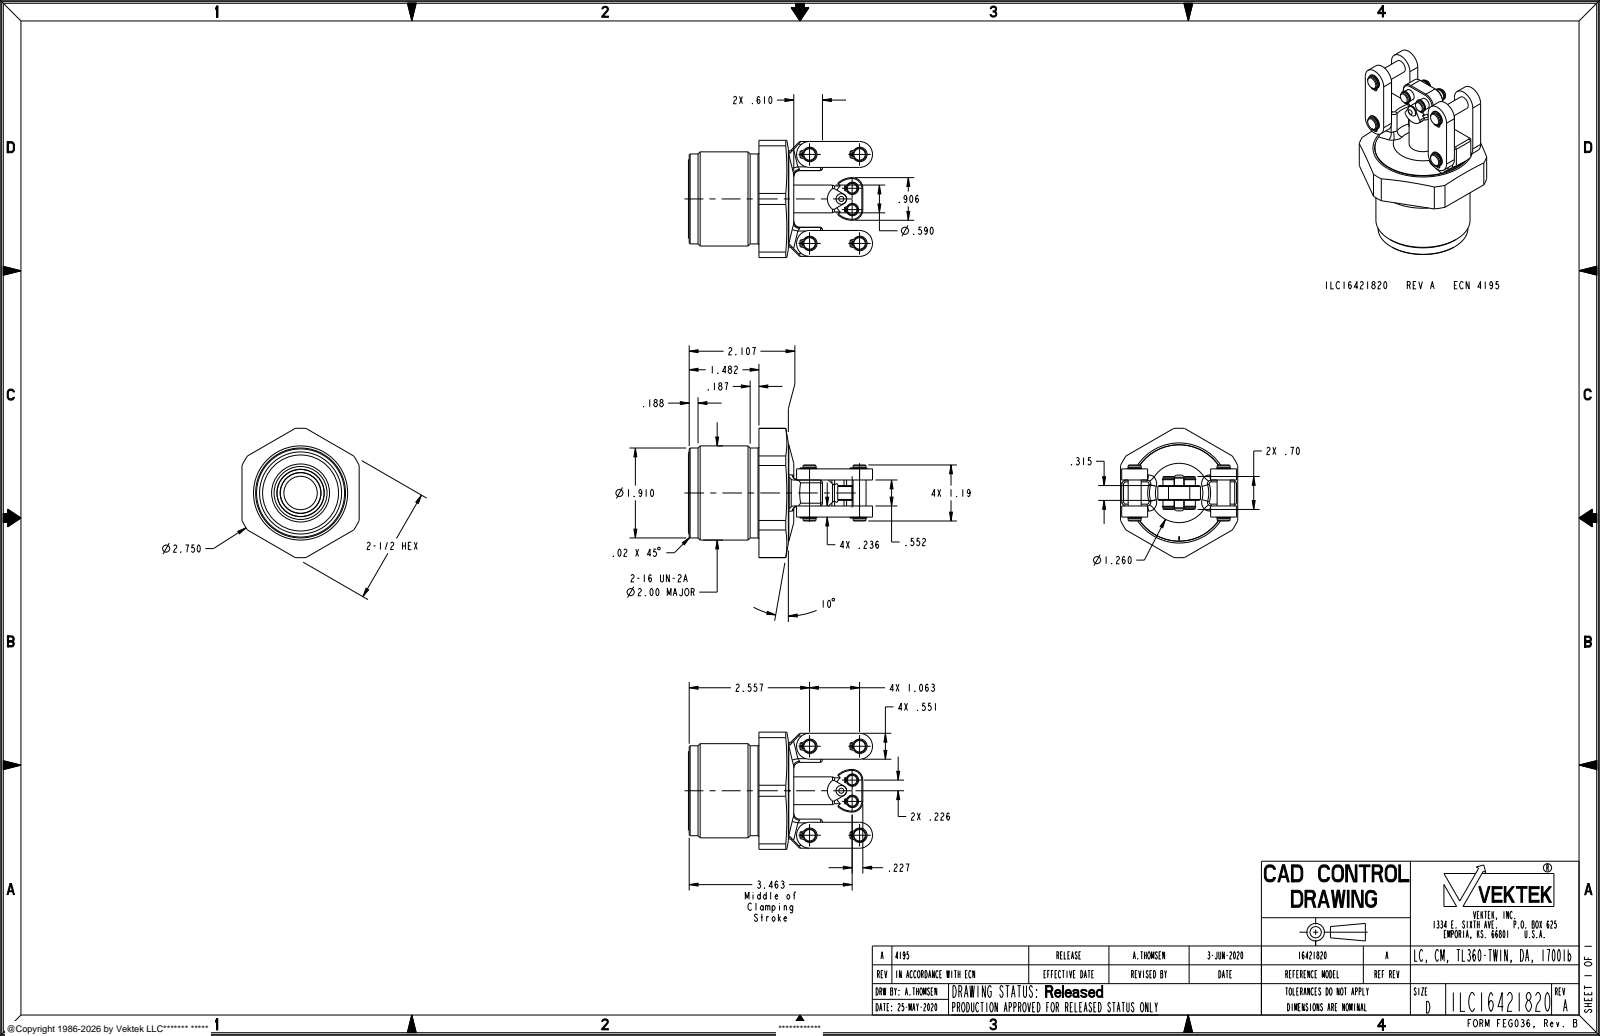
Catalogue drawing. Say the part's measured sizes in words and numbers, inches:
The part is named "ILC164218_0_BODY; ILC16321820_LUG; ILC16421820". Its 3-D file was written by "PRO/ENGINEER BY PARAMETRIC TECHNOLOGY CORPORATION, 2013320 (AUTOMOTIVE_DESIGN)". It is 4 solids with 522 faces: 179 planar, 257 cylindrical and 86 other. Overall it measures 3.912 by 2.75 by 2.49 inches. Its volume is 9.765 cubic inches and its surface area 56.16 square inches. Round holes: 8 of diameter 0.041, 4 of diameter 0.026, 2 of diameter 0.237, 1 of diameter 0.118, 1 of diameter 0.709, 1 of diameter 0.999, 1 of diameter 2.048. Round bosses or shafts: 4 of diameter 0.276, 4 of diameter 0.255, 2 of diameter 0.263, 2 of diameter 0.236, 2 of diameter 0.222, 1 of diameter 2.044, 1 of diameter 2, 1 of diameter 1.91. Partial cylindrical surfaces (rounded edges, fillets, slot ends): 8 of radius 0.041, 8 of radius 0.084, 5 of radius 0.276, 4 of radius 0.026, 4 of radius 0.042, 4 of radius 0.079, 4 of radius 0.154, 2 of radius 0.05. The main face-to-face distances are 0.236, 0.788, 0.248, 2.49, 1.428, 1.676, 1.024, 0.552, 0.024, 2.465. The hole center spacings are 0.08, 0.14, 1.063, 1.066, 1.89, 2.169, 0.452, 0.06.
